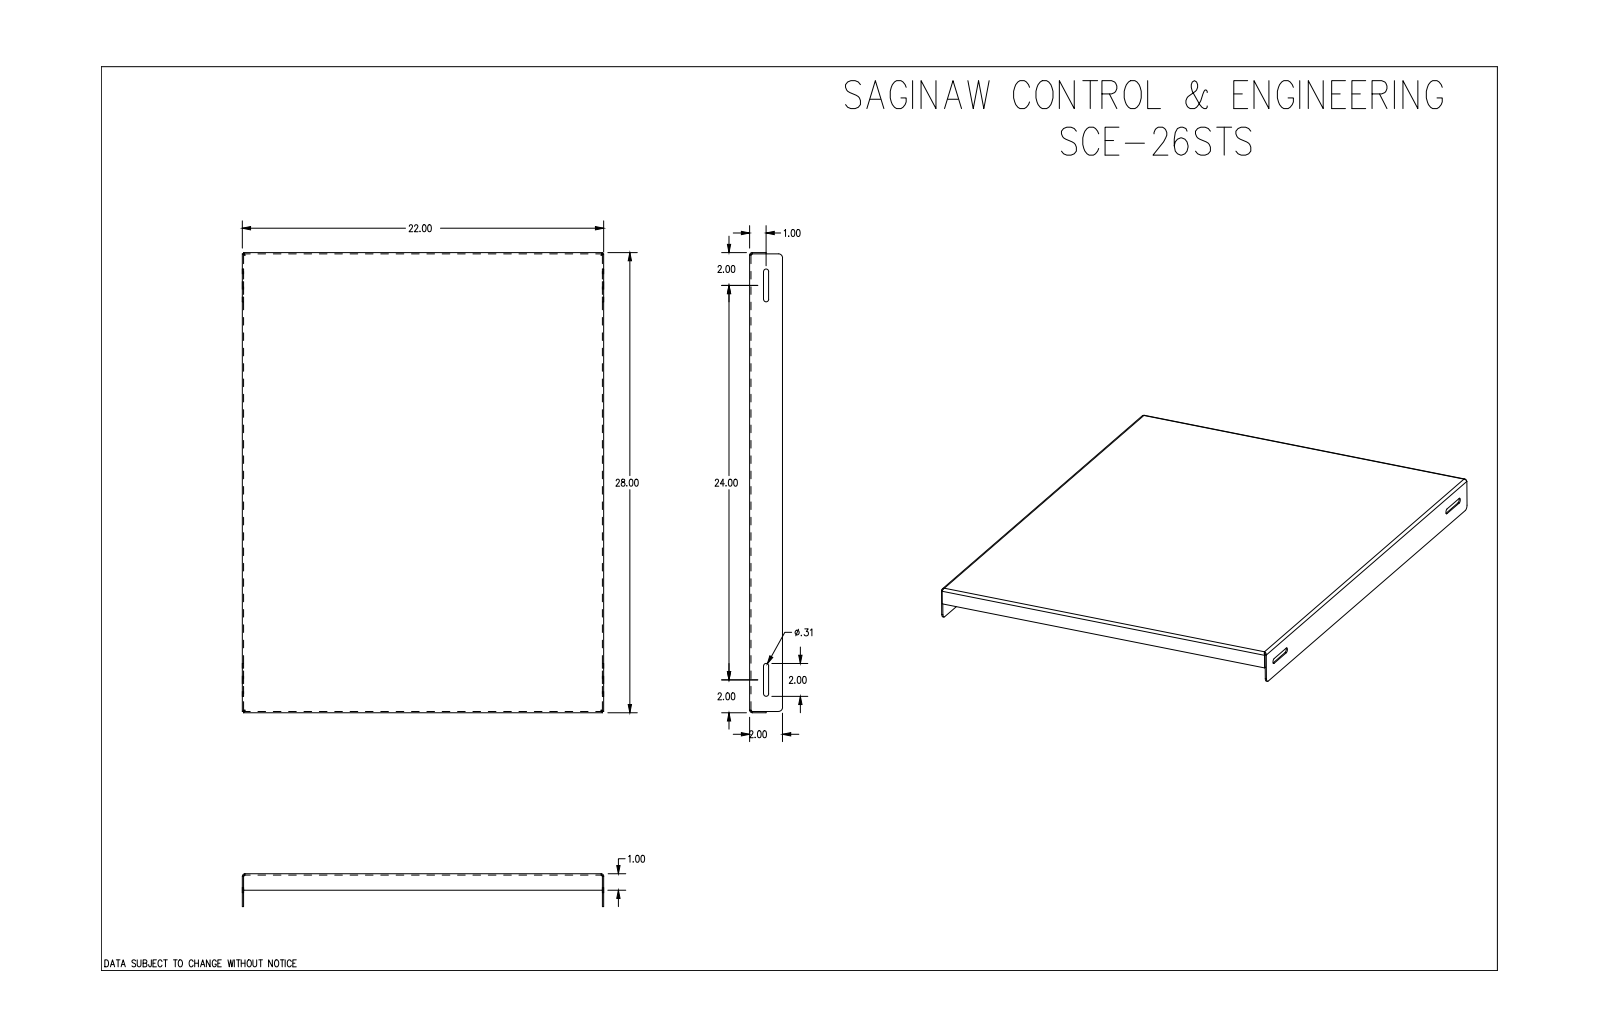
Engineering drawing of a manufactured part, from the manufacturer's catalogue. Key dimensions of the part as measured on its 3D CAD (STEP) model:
Part name (STEP PRODUCT): SCE-26STS
STEP written by: SolidWorks 2019 (CONFIG_CONTROL_DESIGN)
Units: inches
Bodies: 1 solid, 62 faces (30 planar, 24 cylindrical, 8 other)
Overall size (bounding box): 28 × 22 × 2
Volume: 58.95 in³ · Surface area: 1 522 in²
Partial cylindrical surfaces — rounded edges, fillets, slot ends (radius × count): R0.078 ×4, R0.156 ×4, R0.156 ×4, R0.02 ×2, R0.25 ×2
Main face-to-face distances: 0.078, 21.922, 21.844, 22, 27.922, 27.844, 28, 1, 1.922, 2
